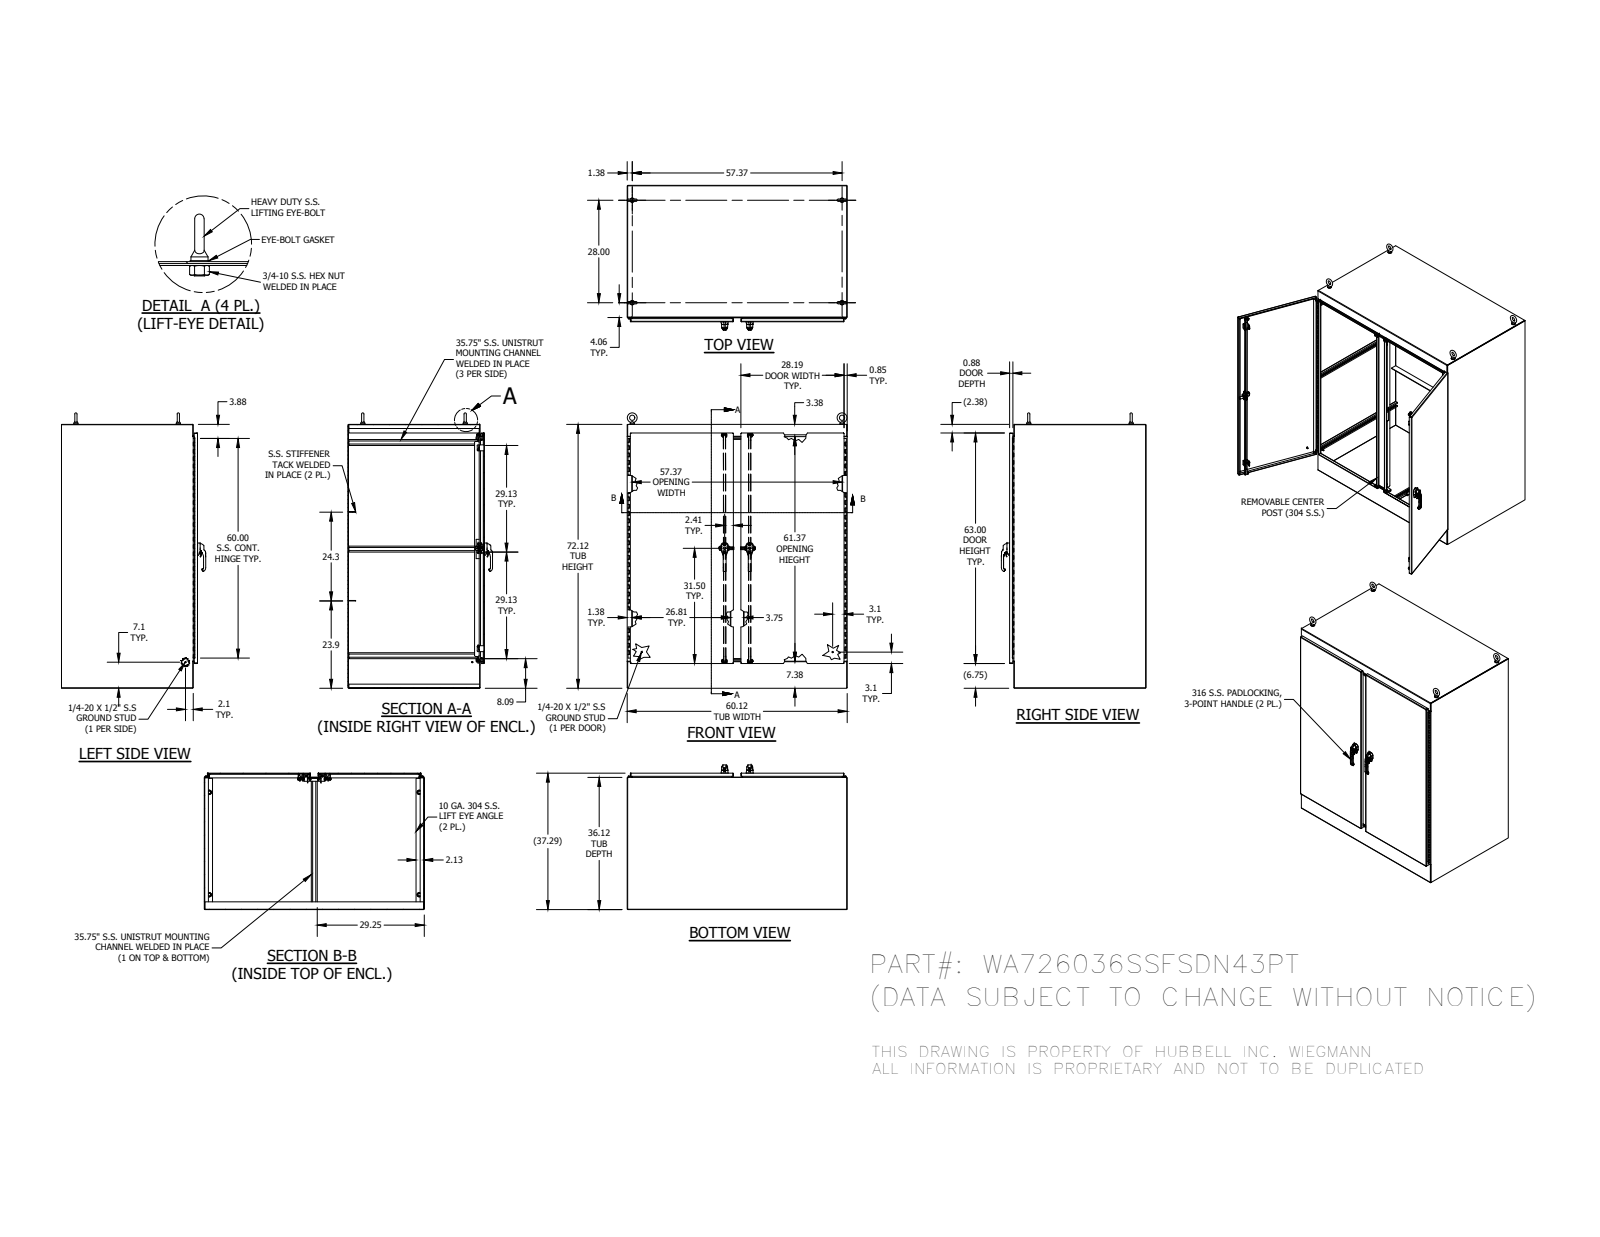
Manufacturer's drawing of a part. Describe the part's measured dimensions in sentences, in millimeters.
The part is named "WA6036SSFSDN43PTTOP; WA7260SSFSDN43PTFB; 7379-M6-8X25_AF0; 1225-05 (+8 more)". Its 3-D file was written by "SolidWorks 2014 (AUTOMOTIVE_DESIGN)". It is 139 solids with 7320 faces: 2662 planar, 2754 cylindrical and 1904 other. Overall it measures 1911.3 by 1527.2 by 1004.3 millimeters. Its volume is 44 700 000 cubic millimeters and its surface area 28 690 000 square millimeters. Round holes: 16 of diameter 6.7, 16 of diameter 9.5, 8 of diameter 4.7, 6 of diameter 5.4, 6 of diameter 7.1, 5 of diameter 6.4, 4 of diameter 5, 4 of diameter 6.1, 4 of diameter 6.4, 4 of diameter 7.1, 4 of diameter 8, 4 of diameter 10.2. Round bosses or shafts: 7 of diameter 6.4, 6 of diameter 13.5, 6 of diameter 6, 5 of diameter 25.4, 4 of diameter 31.8, 4 of diameter 28.4, 4 of diameter 19.1, 4 of diameter 14.3. Partial cylindrical surfaces (rounded edges, fillets, slot ends): 352 of radius 0.5, 214 of radius 0.3, 44 of radius 0.5, 44 of radius 3.2, 34 of radius 1.3, 28 of radius 2, 24 of radius 0.6, 24 of radius 1.5. The main face-to-face distances are 3.2, 3.2, 1524, 1828.8, 944, 1520.8, 1527.2, 1825.6, 914.4, 29.6. The hole center spacings are 1384, 1403.1, 508, 9.7, 9.7, 169.3, 19.3, 338.7.
